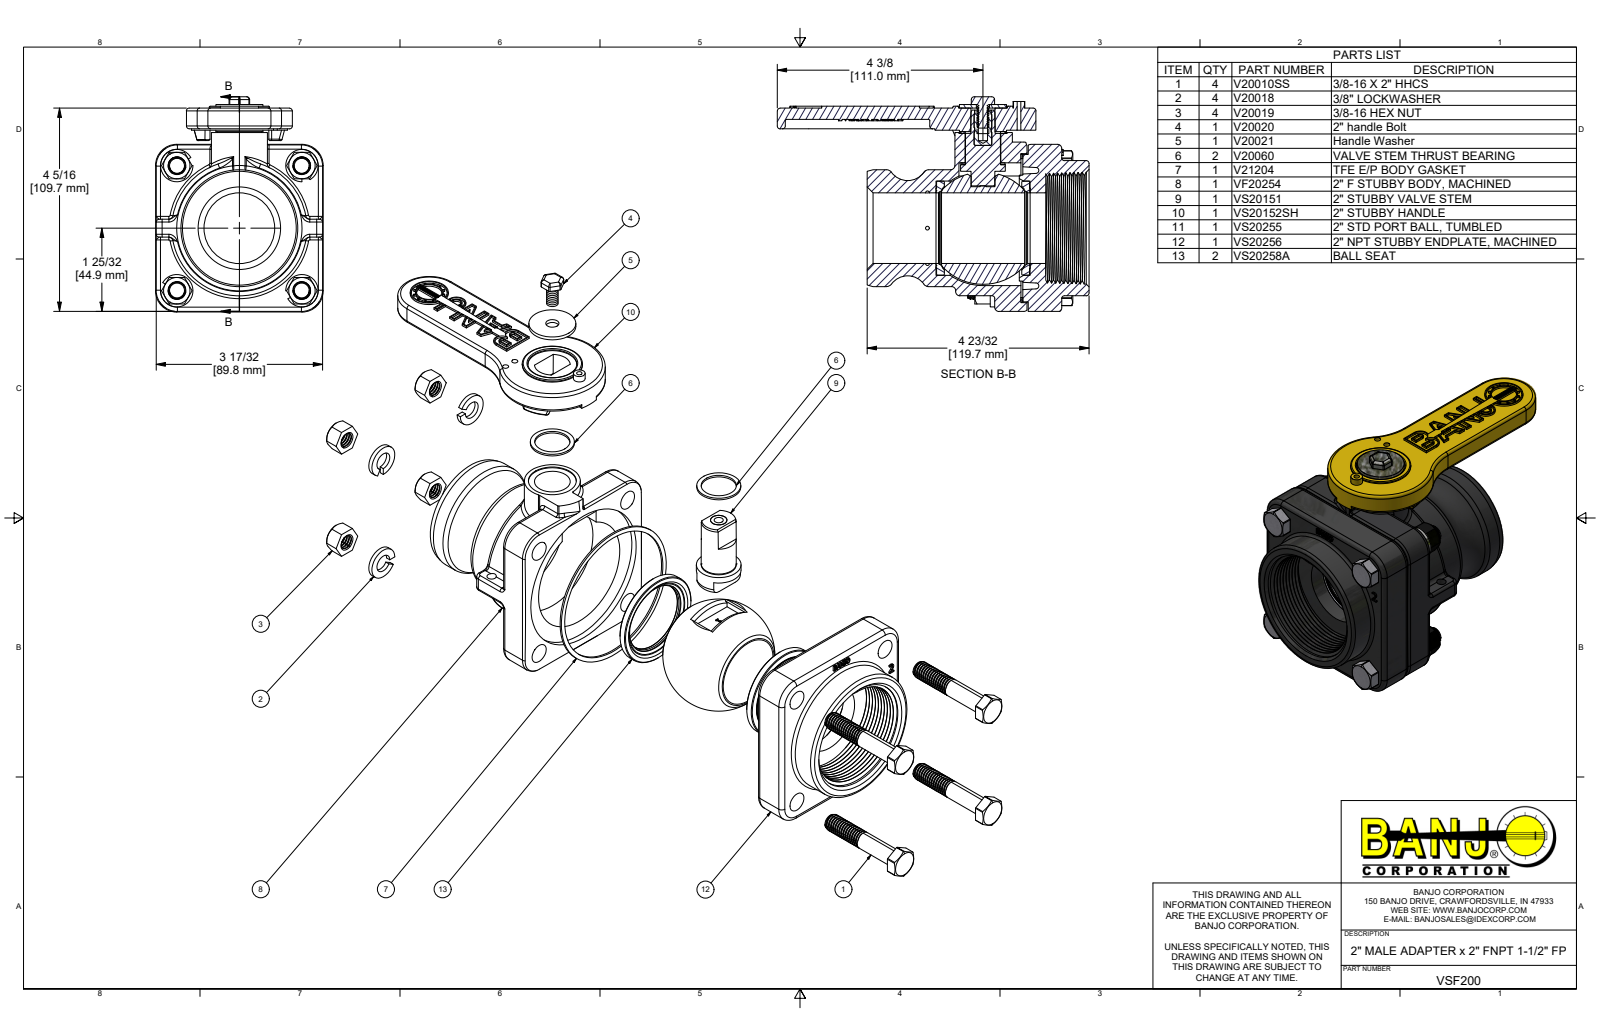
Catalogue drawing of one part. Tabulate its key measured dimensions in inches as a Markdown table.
| quantity | value |
| --- | --- |
| part name | VSF200; VF20254; VXF20254; V20010SS (+8 more) |
| STEP written by | Autodesk Inventor 2018 (AUTOMOTIVE_DESIGN) |
| units | inches |
| bodies | 25 solids, 2512 faces (942 planar, 611 cylindrical, 959 other) |
| overall size | 6.624 × 4.571 × 3.56 |
| volume | 27.86 in³ |
| surface area | 232.8 in² |
| round holes (diameter × count) | 0.406 × 8, 0.375 × 5, 0.307 × 4, 0.385 × 4, 0.08 × 2, 0.13 × 2, 0.2 × 2, 0.118 × 1, 0.196 × 1, 0.281 × 1, 0.351 × 1, 0.544 × 1 |
| round bosses / shafts (diameter × count) | 0.324 × 60, 0.687 × 4, 0.375 × 4, 3.15 × 1, 3.13 × 1, 2.87 × 1, 2.482 × 1, 2.25 × 1 |
| partial cylindrical surfaces (radius × count) | 0.06 × 26, 0.09 × 21, 0.03 × 15, 0.162 × 8, 0.125 × 7, 0.32 × 4, 0.468 × 4, 0.469 × 4 |
| main face-to-face distances | 3.56, 1.424, 0.04, 0.737, 0.27, 0.687, 0.091, 0.828, 0.596, 0.5 |
| hole center spacings | 2.653, 1.872, 1.88, 2.648, 2.658, 3.752, 1.593, 1.816 |
